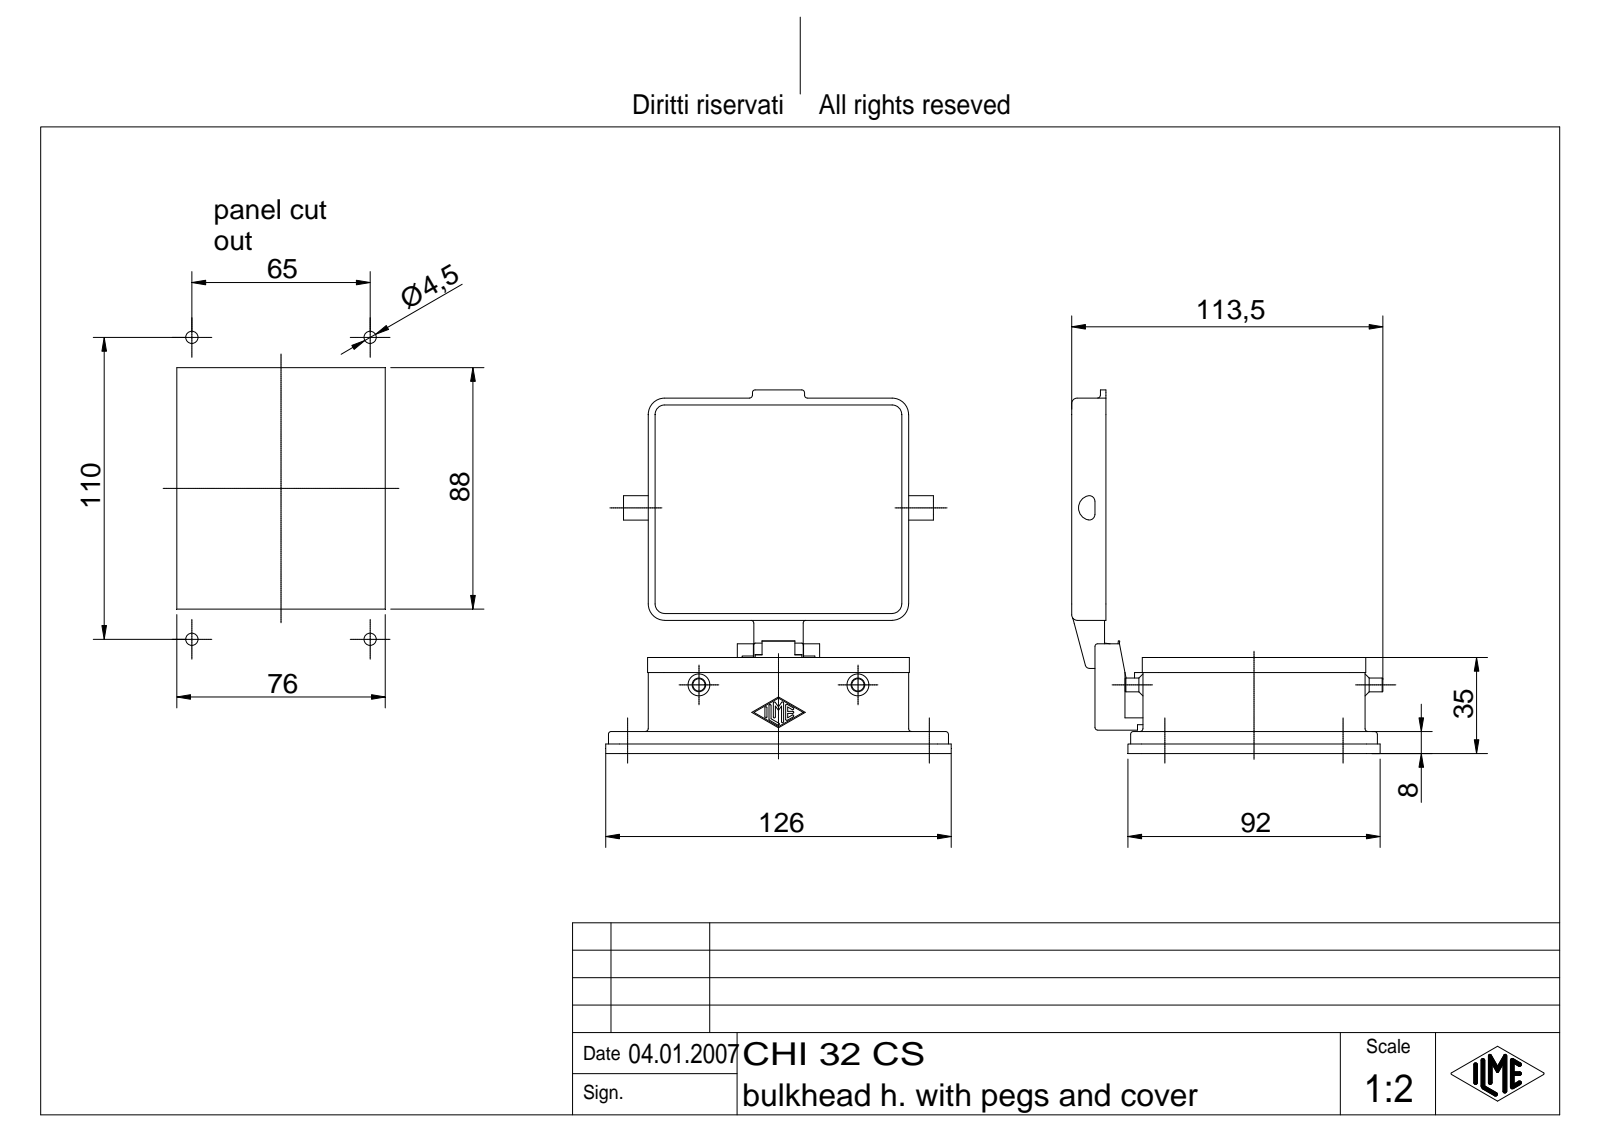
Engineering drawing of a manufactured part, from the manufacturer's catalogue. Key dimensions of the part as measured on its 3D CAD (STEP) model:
Part name (STEP PRODUCT): CHI 32 CS
STEP written by: Autodesk Inventor 7 (AUTOMOTIVE_DESIGN)
Units: millimetres
Bodies: 1 solid, 493 faces (203 planar, 192 cylindrical, 98 other)
Overall size (bounding box): 132.5 × 126 × 113.5
Volume: 117 971 mm³ · Surface area: 67 617 mm²
Round holes (diameter × count): ⌀2.46 ×4, ⌀3.1 ×4, ⌀4.5 ×4, ⌀4.6 ×4, ⌀4 ×1, ⌀5 ×1
Round bosses / shafts (diameter × count): ⌀5 ×2, ⌀3 ×2, ⌀7 ×1
Partial cylindrical surfaces — rounded edges, fillets, slot ends (radius × count): R1 ×19, R0.38 ×14, R2 ×12, R6 ×12, R0.5 ×11, R3.5 ×8, R1.5 ×5, R2.5 ×4
Main face-to-face distances: 3.5, 3, 92, 78, 8, 4, 2.5, 104, 1, 25.5
Hole centre spacings: 16.28, 27, 32.37, 40.41, 65, 66.03, 77.5, 82.07
